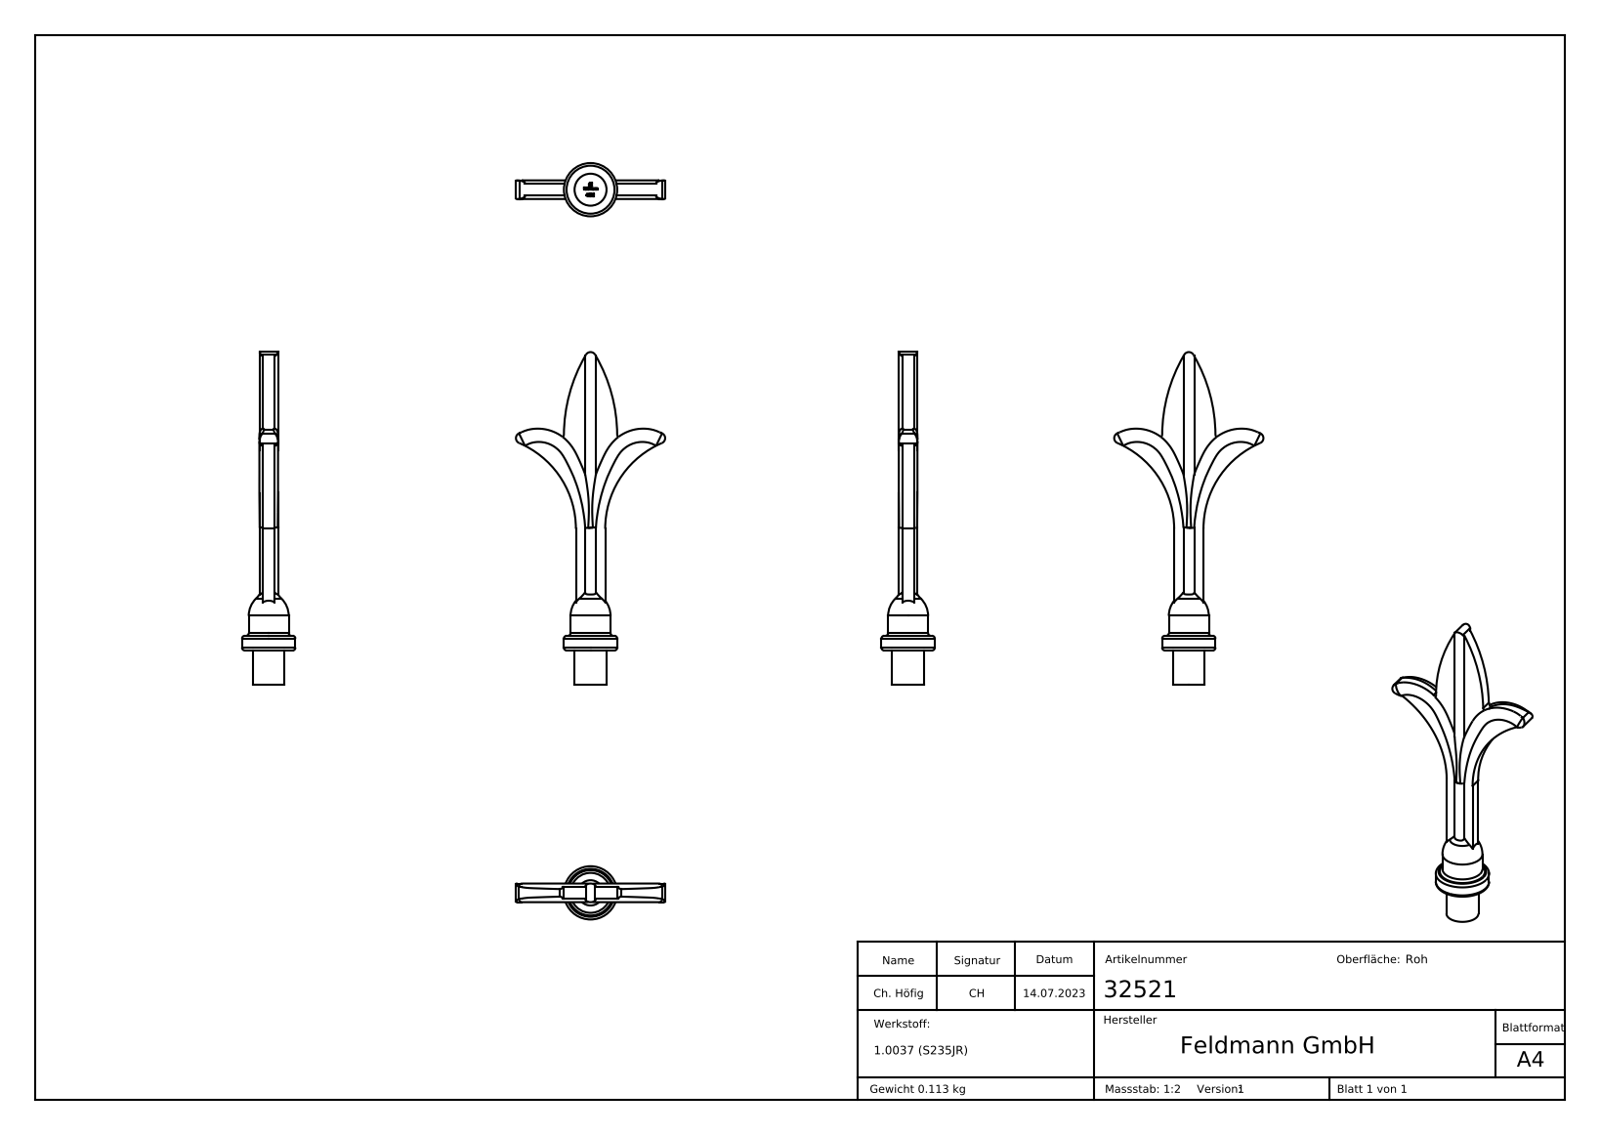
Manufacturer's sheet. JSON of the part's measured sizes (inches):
{"part_name": "32521", "step_written_by": "SolidWorks 2018 (CONFIG_CONTROL_DESIGN)", "units": "inches", "bodies": {"solids": 1, "faces": 271, "planar": 137, "cylindrical": 14, "other": 120}, "overall_size": [4.921, 2.205, 0.787], "volume_in3": 0.882, "surface_area_in2": 10.46, "round_bosses_or_shafts": [[0.787, 1], [0.591, 1], [0.472, 1]], "partial_cylinders_radius": [[0.079, 3], [0.039, 2], [0.591, 2], [1.378, 2], [2.362, 2]], "face_to_face_distances": [0.177, 0.433, 0.512, 0.728, 0.217, 0.508, 0.724, 0.088, 0.029, 0.074]}
